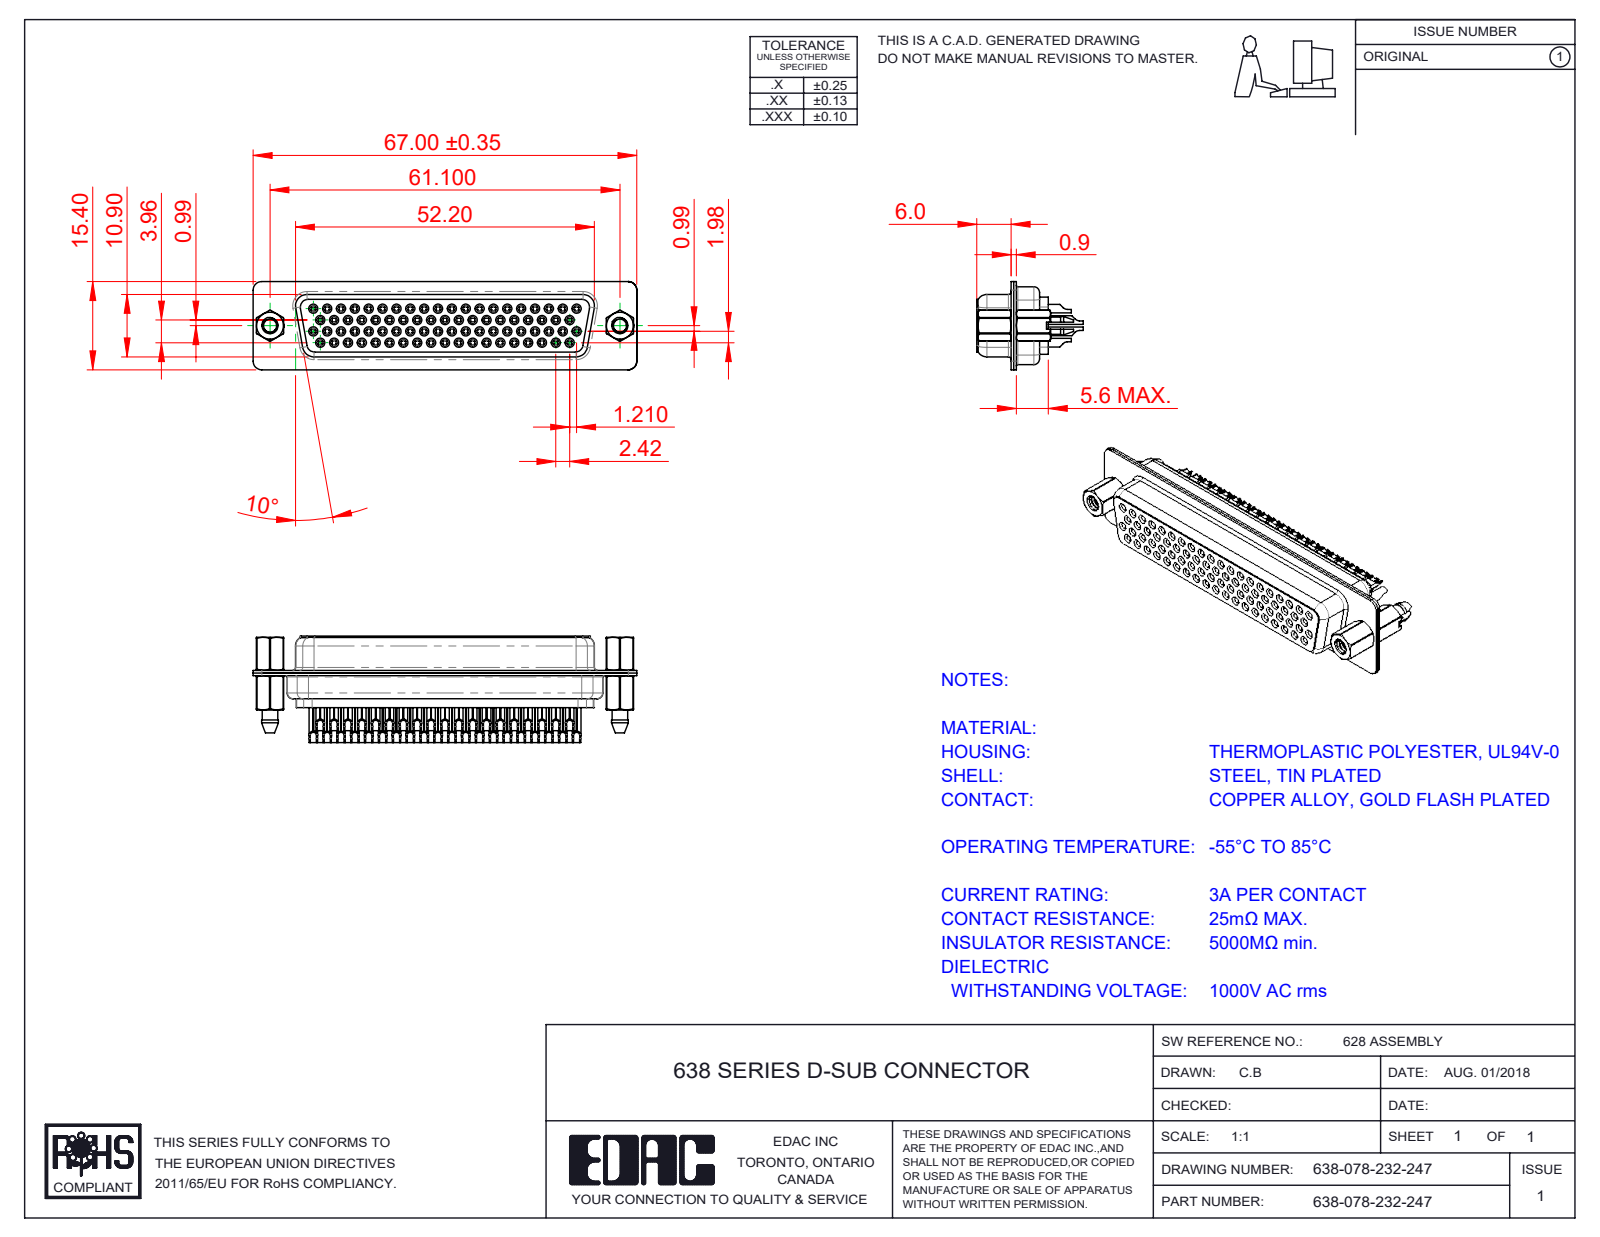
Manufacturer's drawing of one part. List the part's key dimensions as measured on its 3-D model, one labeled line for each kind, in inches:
Part name (STEP PRODUCT): 638 Shell Front_78 Contacts; 638 Housing_78 Contacts; 638 4-40 Threaded Boardlock_LP; 638 Contact Row 1_32(78) (+6 more)
STEP written by: SolidWorks 2020 (CONFIG_CONTROL_DESIGN)
Units: inches
Bodies: 85 solids, 7421 faces (1759 planar, 2191 cylindrical, 3471 other)
Overall size (bounding box): 2.638 × 0.732 × 0.606
Volume: 0.388 in³ · Surface area: 35.48 in²
Round holes (diameter × count): ⌀0.031 ×78, ⌀0.039 ×78, ⌀0.043 ×78, ⌀0.063 ×78, ⌀0.067 ×78, ⌀0.071 ×78, ⌀0.089 ×2, ⌀0.09 ×2, ⌀0.157 ×2, ⌀0.159 ×2, ⌀0.191 ×2
Round bosses / shafts (diameter × count): ⌀0.079 ×78, ⌀0.059 ×78, ⌀0.047 ×78, ⌀0.195 ×2, ⌀0.189 ×2, ⌀0.11 ×2, ⌀0.157 ×1
Partial cylindrical surfaces — rounded edges, fillets, slot ends (radius × count): R0.011 ×39, R0.059 ×18, R0.079 ×12, R0.039 ×8, R0.061 ×8, R0.01 ×4, R0.02 ×4, R0.022 ×4
Main face-to-face distances: 0.018, 0.016, 0.035, 0.053, 0.378, 0.465, 0.071, 0.449, 0.087, 0.518
Hole centre spacings: 0.095, 0.191, 0.286, 0.381, 0.239, 0.476, 0.274, 0.334
